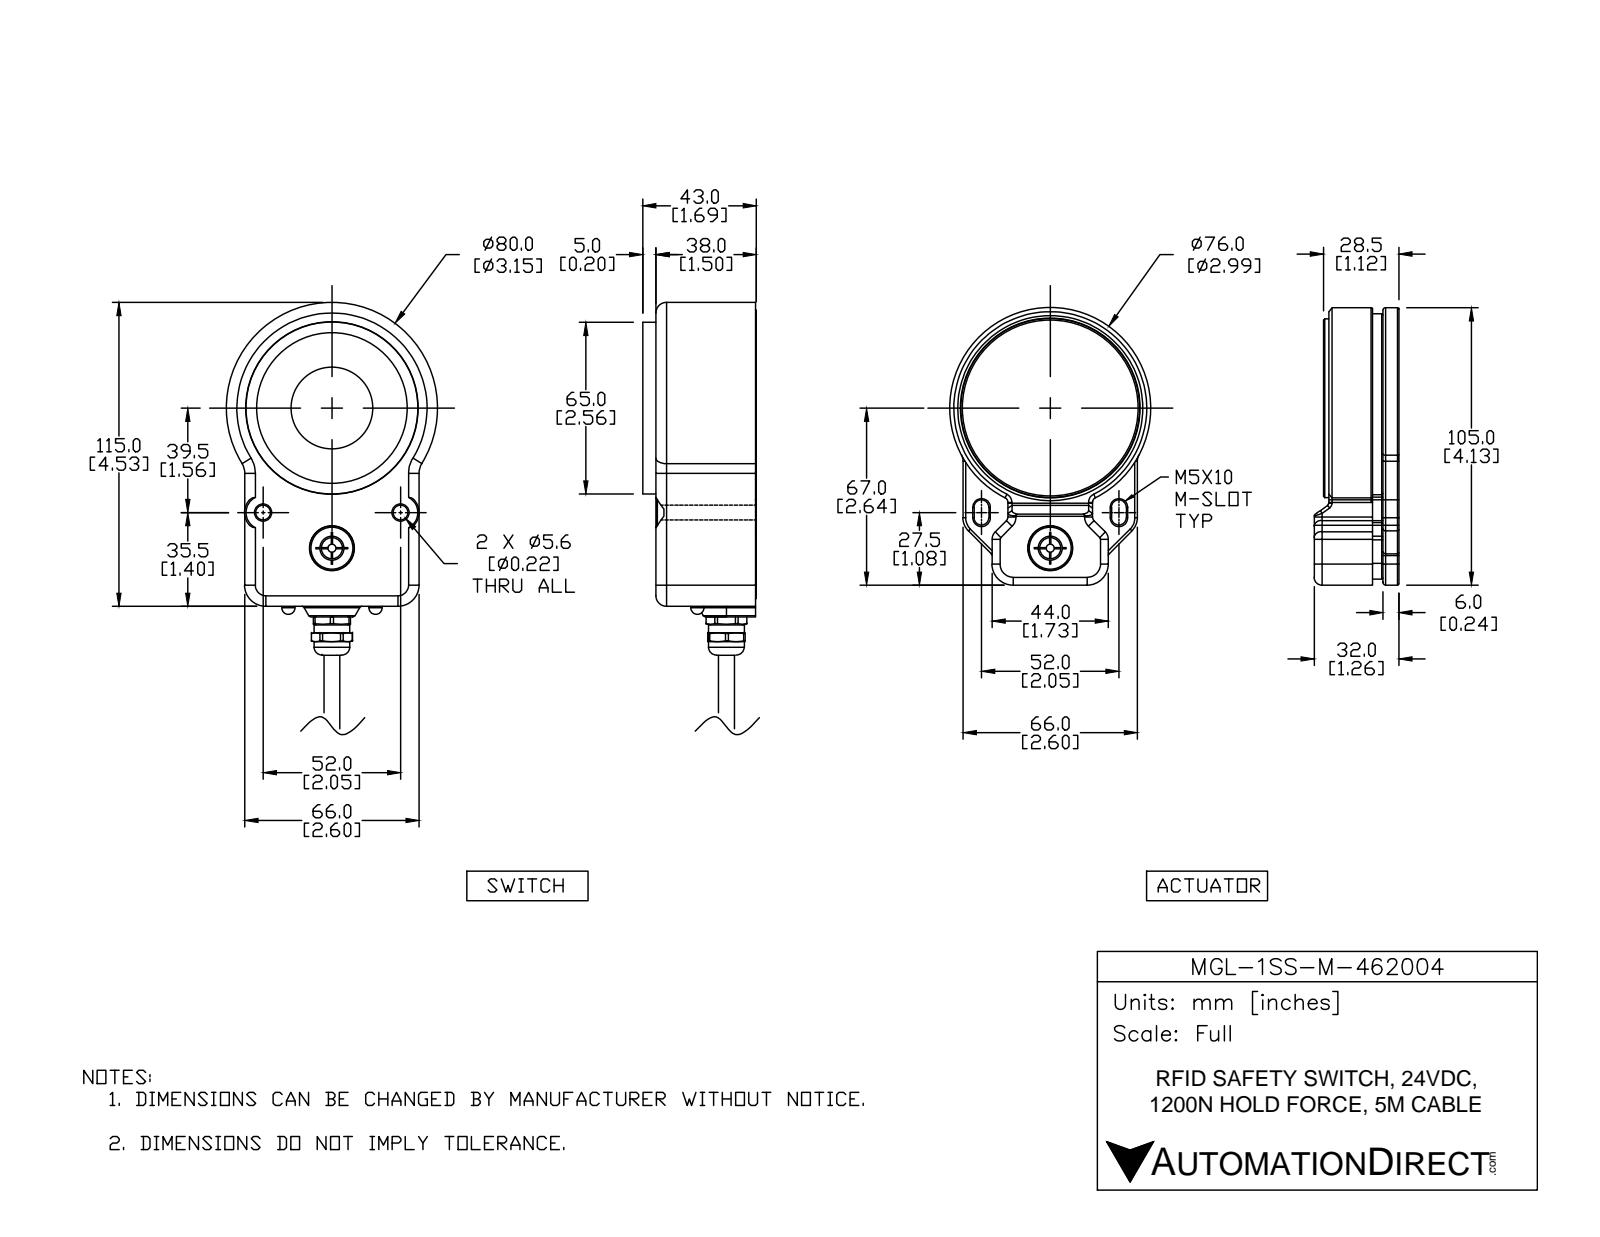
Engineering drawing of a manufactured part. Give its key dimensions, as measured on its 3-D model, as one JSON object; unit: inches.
{"part_name": "MGL-1SS-M-462004_1; MGL-1SS-M-462004; MGL-1SS-M-462004_2", "step_written_by": "SolidWorks 2017 (AUTOMOTIVE_DESIGN)", "units": "inches", "bodies": {"solids": 19, "faces": 1647, "planar": 423, "cylindrical": 679, "other": 545}, "overall_size": [8.465, 3.15, 2.854], "volume_in3": 19.52, "surface_area_in2": 219.9, "round_holes": [[0.098, 8], [0.13, 6], [0.197, 6], [0.453, 5], [0.157, 3], [0.315, 3], [0.354, 3], [0.22, 2], [0.276, 2], [0.252, 1], [0.266, 1], [0.268, 1]], "round_bosses_or_shafts": [[0.02, 4], [0.472, 2], [0.228, 2], [0.22, 2], [0.118, 2], [0.047, 2], [2.992, 1], [2.811, 1]], "partial_cylinders_radius": [[0.02, 188], [0.039, 64], [0.079, 26], [0.012, 17], [0.118, 13], [0.157, 12], [0.217, 10], [0.024, 7]], "face_to_face_distances": [0.236, 0.315, 0.098, 0.413, 1.378, 2.303, 1.122, 0.118, 0.354, 2.205], "hole_center_spacings": [1.392, 1.969, 0.984, 1.28, 1.537, 0.787, 1.364, 0.349]}
